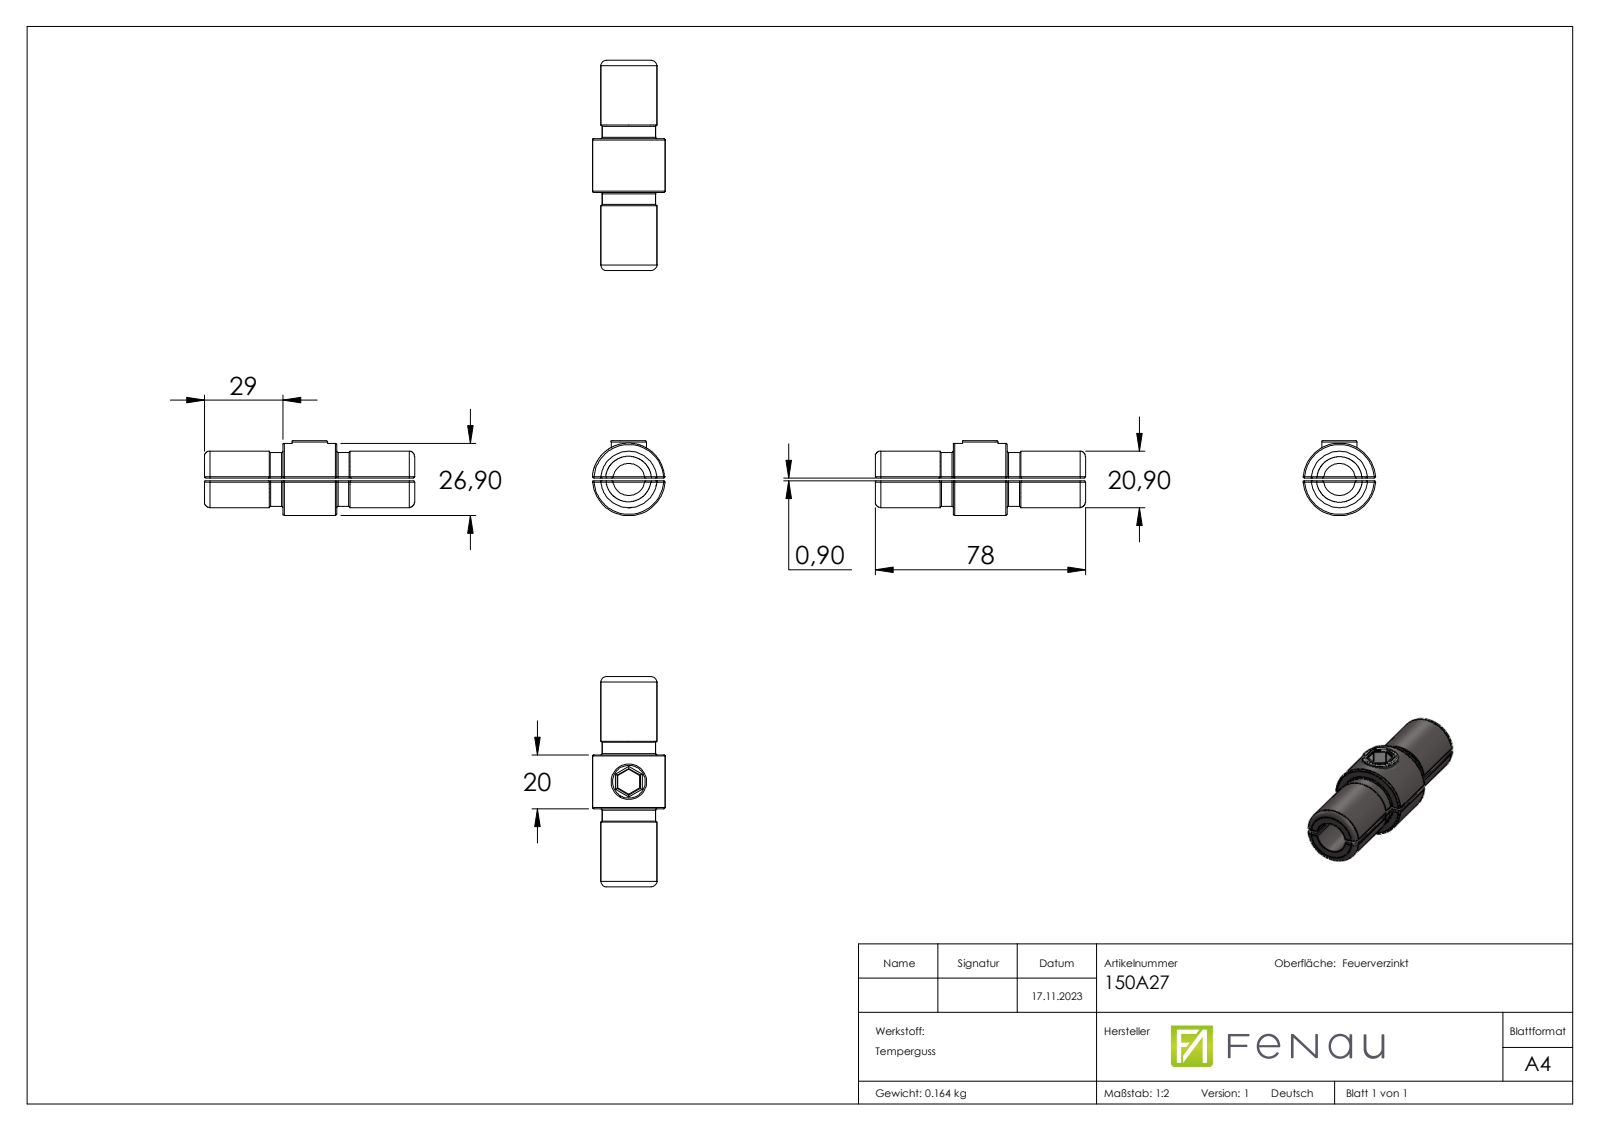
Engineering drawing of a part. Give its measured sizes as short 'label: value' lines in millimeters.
name: 150-A27 Teil1_150-A27 Teil1; 150-A27; 150-A27 Teil3; 150-A27 Teil2_150-A27 Teil2
written by: SolidWorks 2018 (CONFIG_CONTROL_DESIGN)
unit: mm
bodies: 3 solids, 187 faces (45 planar, 86 cylindrical, 56 other)
size: 78 × 27.9 × 26.83
volume: 22 342 mm³; area: 11 751 mm²
holes: 1× ⌀11.8, 1× ⌀11.9, 1× ⌀15
bosses: 1× ⌀26.9, 1× ⌀20.9, 1× ⌀13.16
rounds: 28× R0.5, 12× R1
face distances: 0.9, 20, 29, 49, 8.1, 78, 14.9, 14, 1.9, 1
